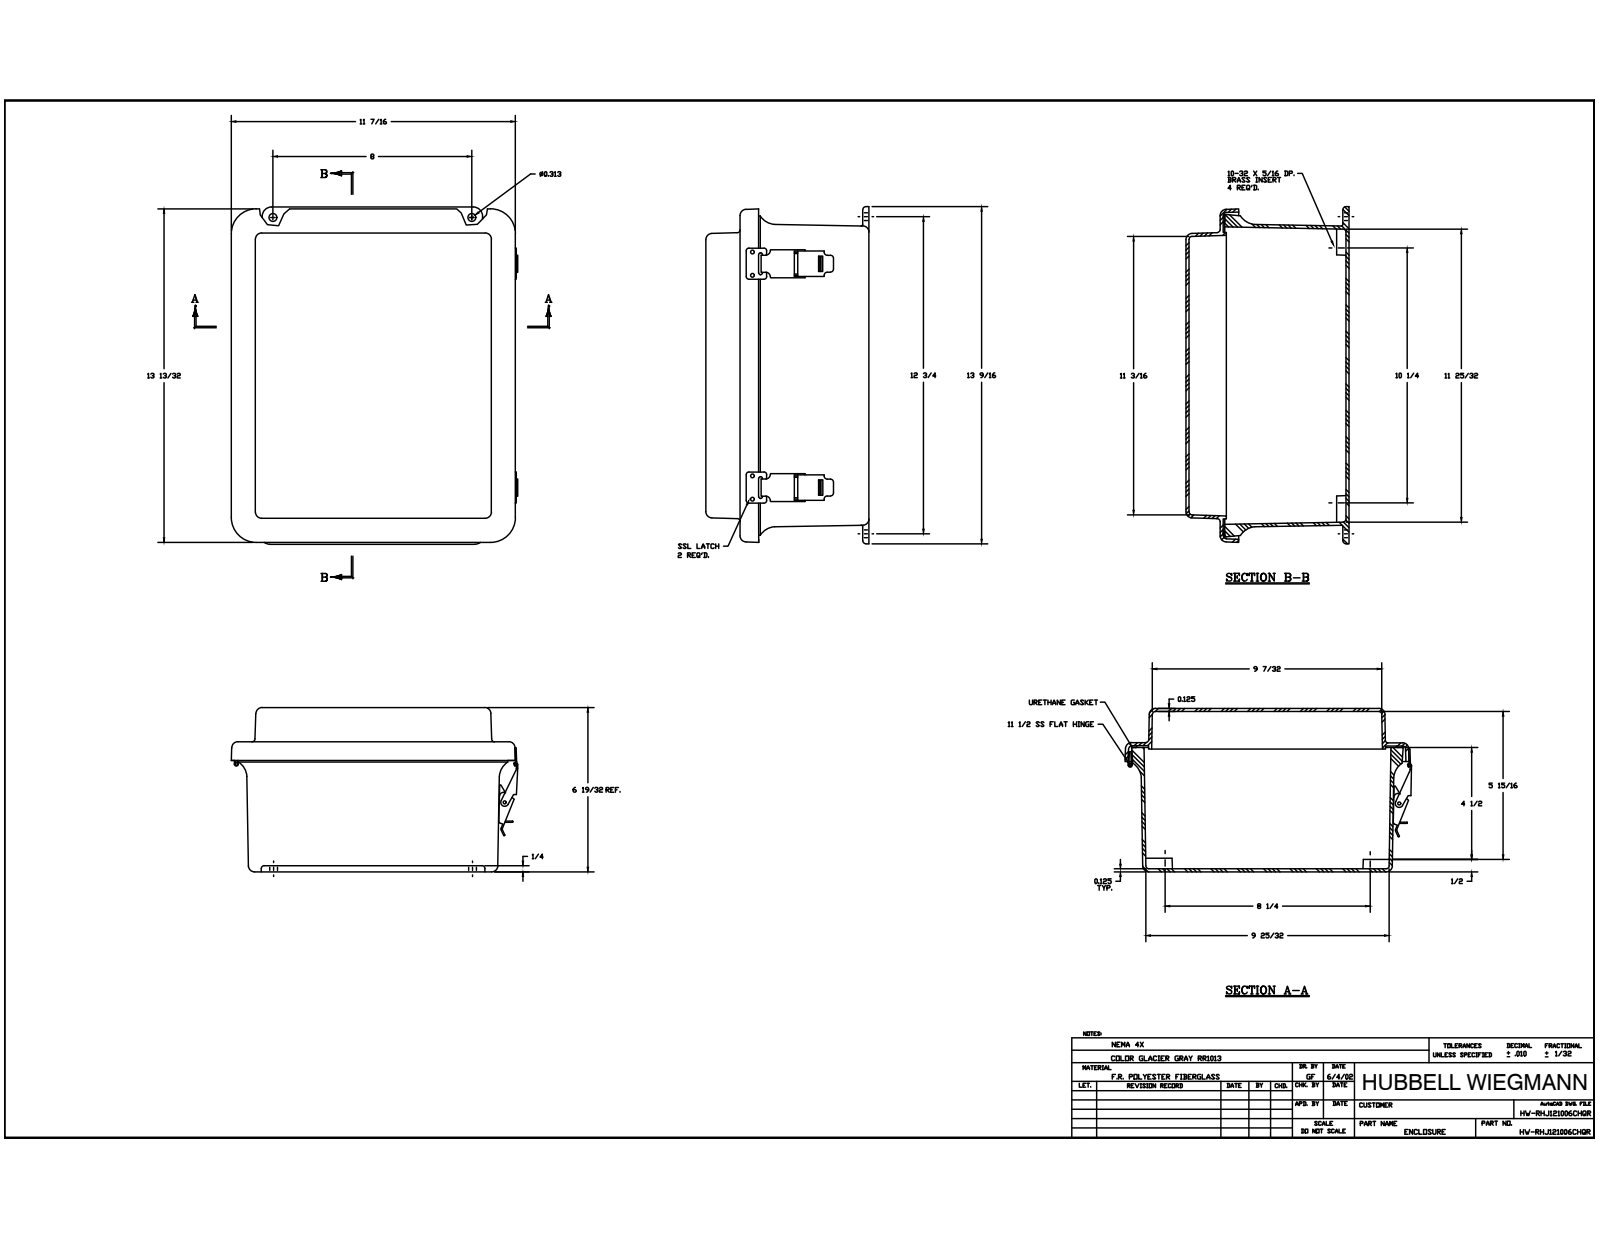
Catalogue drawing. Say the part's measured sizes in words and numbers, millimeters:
The part is named "J1210HL_6; RMINS45821P_177; RMINS45821P_178; RMINS45821P_179 (+8 more)". Its 3-D file was written by "Autodesk Inventor 2014 (AUTOMOTIVE_DESIGN)". It is 38 solids with 1046 faces: 446 planar, 429 cylindrical and 171 other. Overall it measures 344.49 by 293.04 by 167.33 millimeters. Its volume is 1 511 000 cubic millimeters and its surface area 844 428 square millimeters. Round holes: 20 of diameter 3.56, 8 of diameter 2.64, 8 of diameter 3.33, 5 of diameter 3.86, 4 of diameter 3.3, 4 of diameter 3.96, 4 of diameter 5.54, 2 of diameter 3.43, 2 of diameter 9.52, 1 of diameter 2.16, 1 of diameter 2.16. Round bosses or shafts: 16 of diameter 3.17, 8 of diameter 6.35, 4 of diameter 6.86, 1 of diameter 7.62, 1 of diameter 4.31, 1 of diameter 3.94, 1 of diameter 3.05. Partial cylindrical surfaces (rounded edges, fillets, slot ends): 28 of radius 3.17, 20 of radius 0.38, 20 of radius 0.79, 16 of radius 1.14, 12 of radius 0.76, 12 of radius 6.35, 9 of radius 0.57, 6 of radius 1.52. The main face-to-face distances are 3.18, 164.15, 167.33, 160.97, 128.92, 35.23, 125.74, 38.41, 132.1, 32.05. The hole center spacings are 228.6, 229.39, 23.81, 19.05, 92.08, 6.35, 19.04, 34.24.
